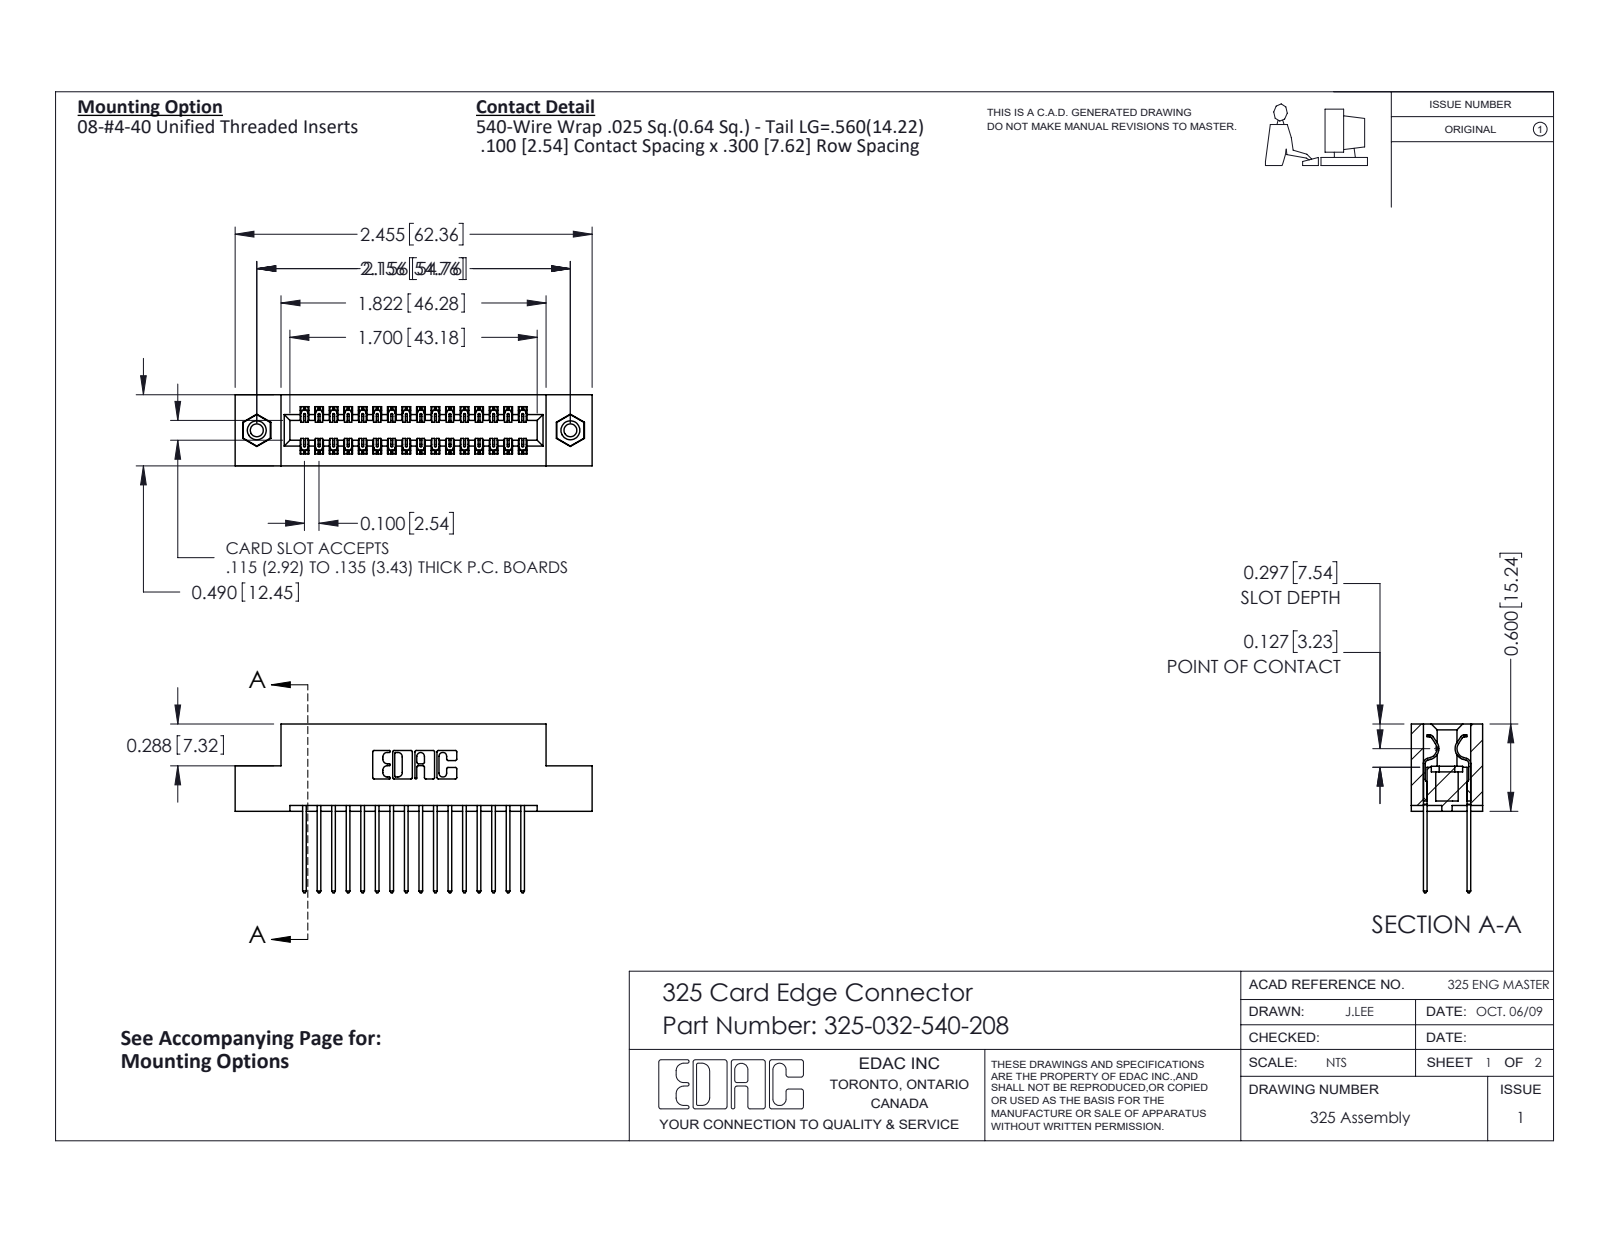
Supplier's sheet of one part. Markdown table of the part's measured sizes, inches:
| quantity | value |
| --- | --- |
| part name | 325-032-540-208; 325 Part_TI; 345-250-001_345-250-003-102; 325-292-001_325-293-140 |
| STEP written by | SolidWorks 2016 (CONFIG_CONTROL_DESIGN) |
| units | inches |
| bodies | 35 solids, 1838 faces (1254 planar, 568 cylindrical, 16 other) |
| overall size | 2.455 × 1.16 × 0.49 |
| volume | 0.484 in³ |
| surface area | 14.84 in² |
| round holes (diameter × count) | 0.089 × 2, 0.125 × 2, 0.16 × 2 |
| round bosses / shafts (diameter × count) | 0.155 × 2 |
| partial cylindrical surfaces (radius × count) | 0.006 × 48, 0.01 × 32, 0.01 × 22, 0.007 × 6, 0.031 × 6, 0.026 × 3, 0.014 × 2, 0.022 × 2 |
| main face-to-face distances | 0.083, 0.407, 0.3, 0.107, 0.383, 0.025, 0.49, 0.325, 0.04, 0.6 |
| hole center spacings | 2.156 |
